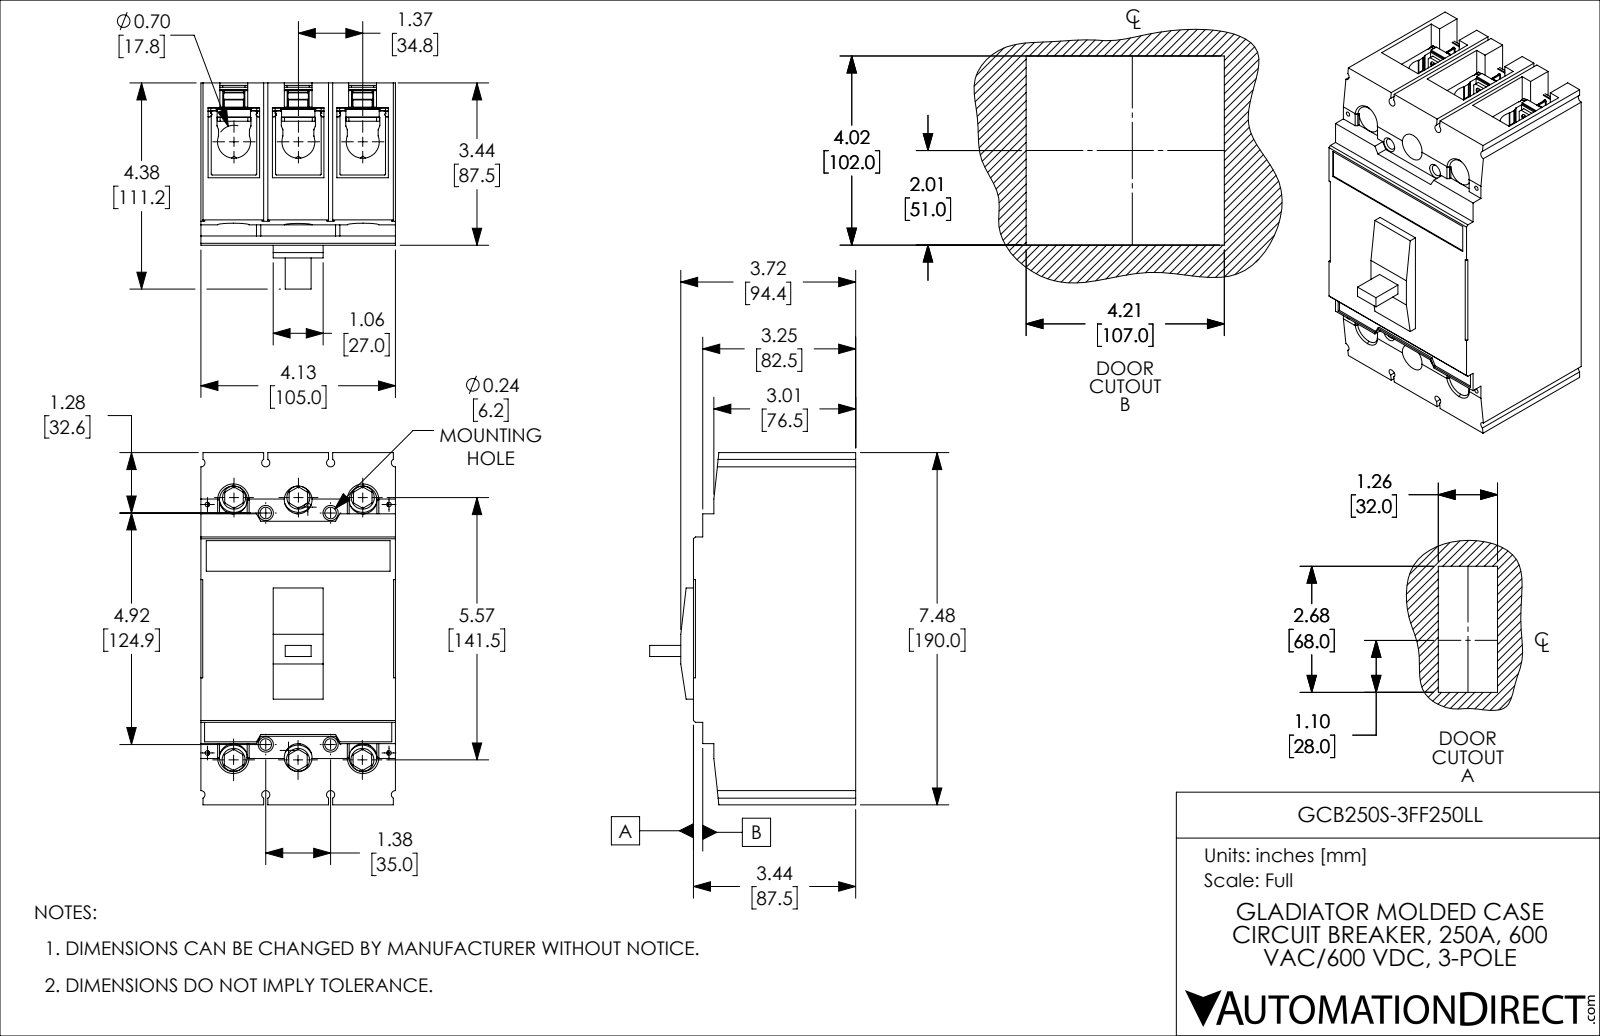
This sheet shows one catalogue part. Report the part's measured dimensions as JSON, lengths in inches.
{"part_name": "GCB250S-3FF250LL", "step_written_by": "SolidWorks 2021 (CONFIG_CONTROL_DESIGN)", "units": "inches", "bodies": {"solids": 25, "faces": 2233, "planar": 975, "cylindrical": 958, "other": 300}, "overall_size": [7.48, 4.378, 4.134], "volume_in3": 87.11, "surface_area_in2": 315.7, "round_holes": [[0.067, 24], [0.157, 24], [0.098, 10], [0.354, 6], [0.591, 6], [0.689, 6], [0.173, 4], [0.244, 4]], "round_bosses_or_shafts": [[0.709, 6]], "partial_cylinders_radius": [[0.012, 206], [0.039, 72], [0.059, 36], [0.02, 26], [0.008, 24], [0.079, 20], [0.016, 12], [0.031, 12]], "face_to_face_distances": [1.368, 4.134, 2.736, 1.094, 0.843, 0.252, 0.059, 1.378, 6.102, 3.445], "hole_center_spacings": [0.285, 0.743, 1.046, 1.378, 5.24, 6.298, 1.368, 1.426]}
